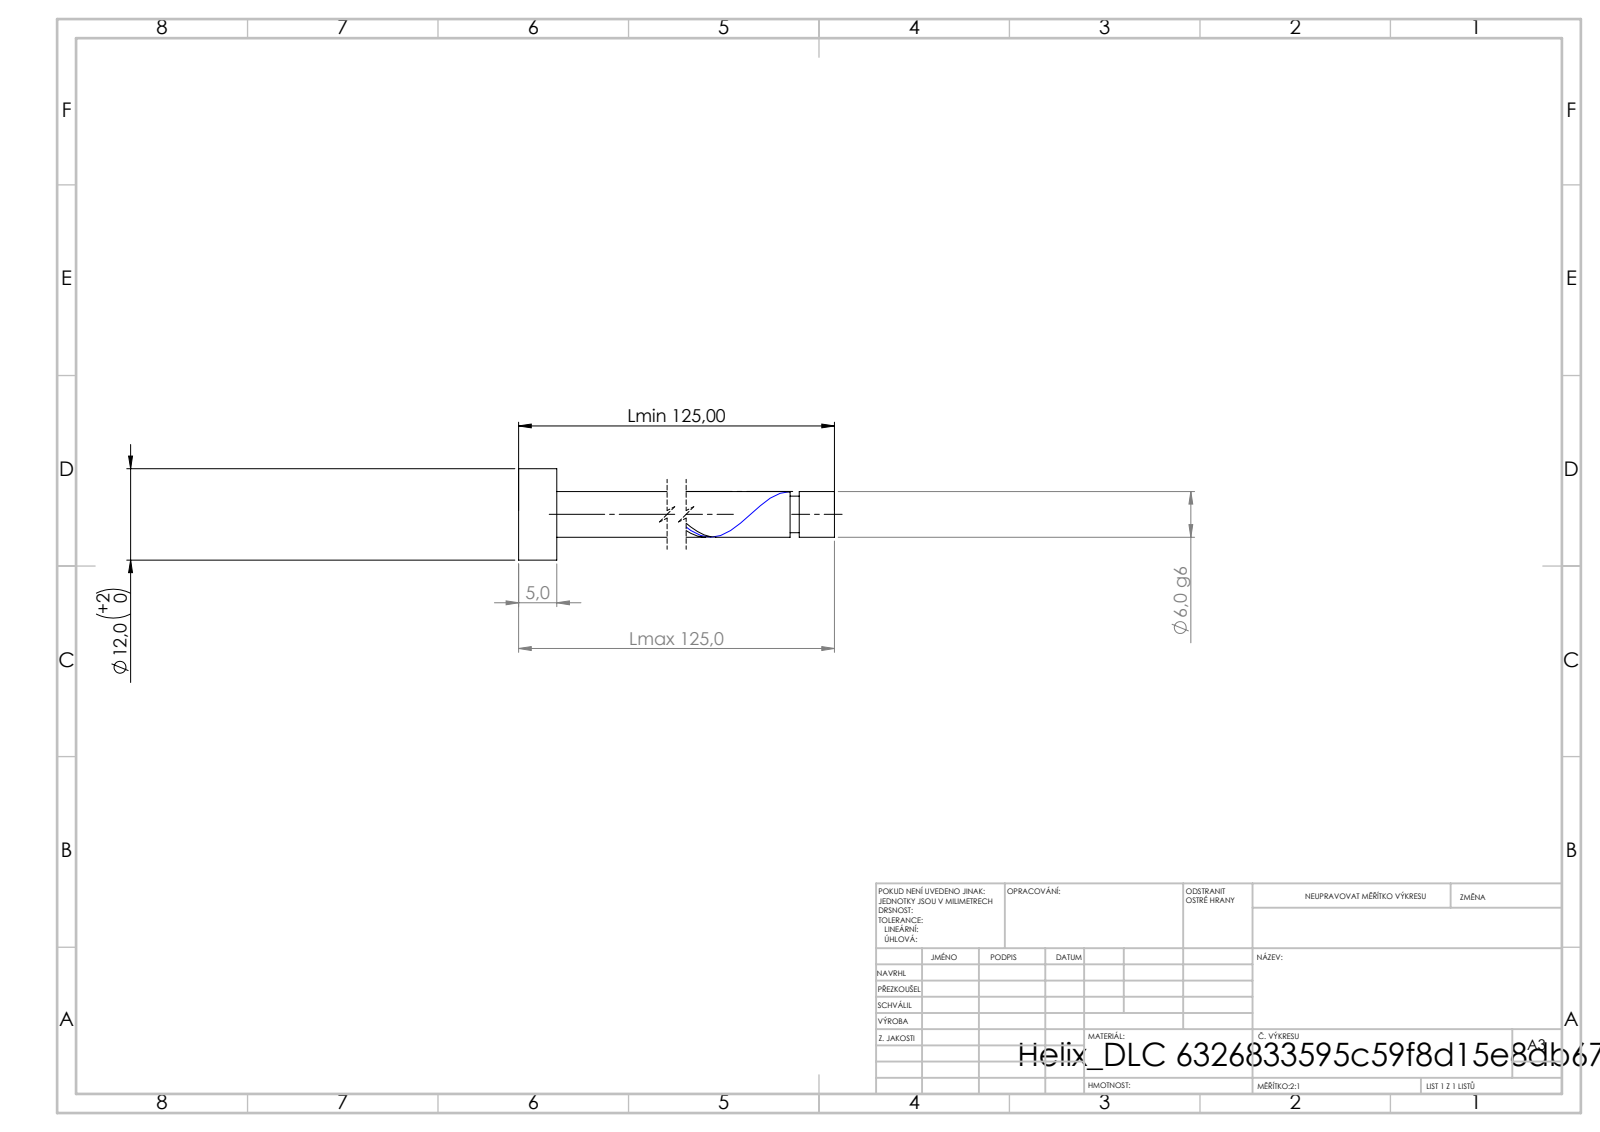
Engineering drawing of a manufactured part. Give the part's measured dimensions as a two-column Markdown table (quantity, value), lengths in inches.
| quantity | value |
| --- | --- |
| STEP written by | SolidWorks 2019 (CONFIG_CONTROL_DESIGN) |
| units | inches |
| bodies | 1 solid, 21 faces (6 planar, 14 cylindrical, 1 other) |
| overall size | 4.921 × 0.472 × 0.472 |
| volume | 0.239 in³ |
| surface area | 4.256 in² |
| round bosses / shafts (diameter × count) | 0.472 × 1, 0.236 × 1, 0.189 × 1 |
| main face-to-face distances | 0.197, 4.921, 4.724, 4.739, 4.543, 0.182, 4.692, 4.495, 0.047, 0.229 |
